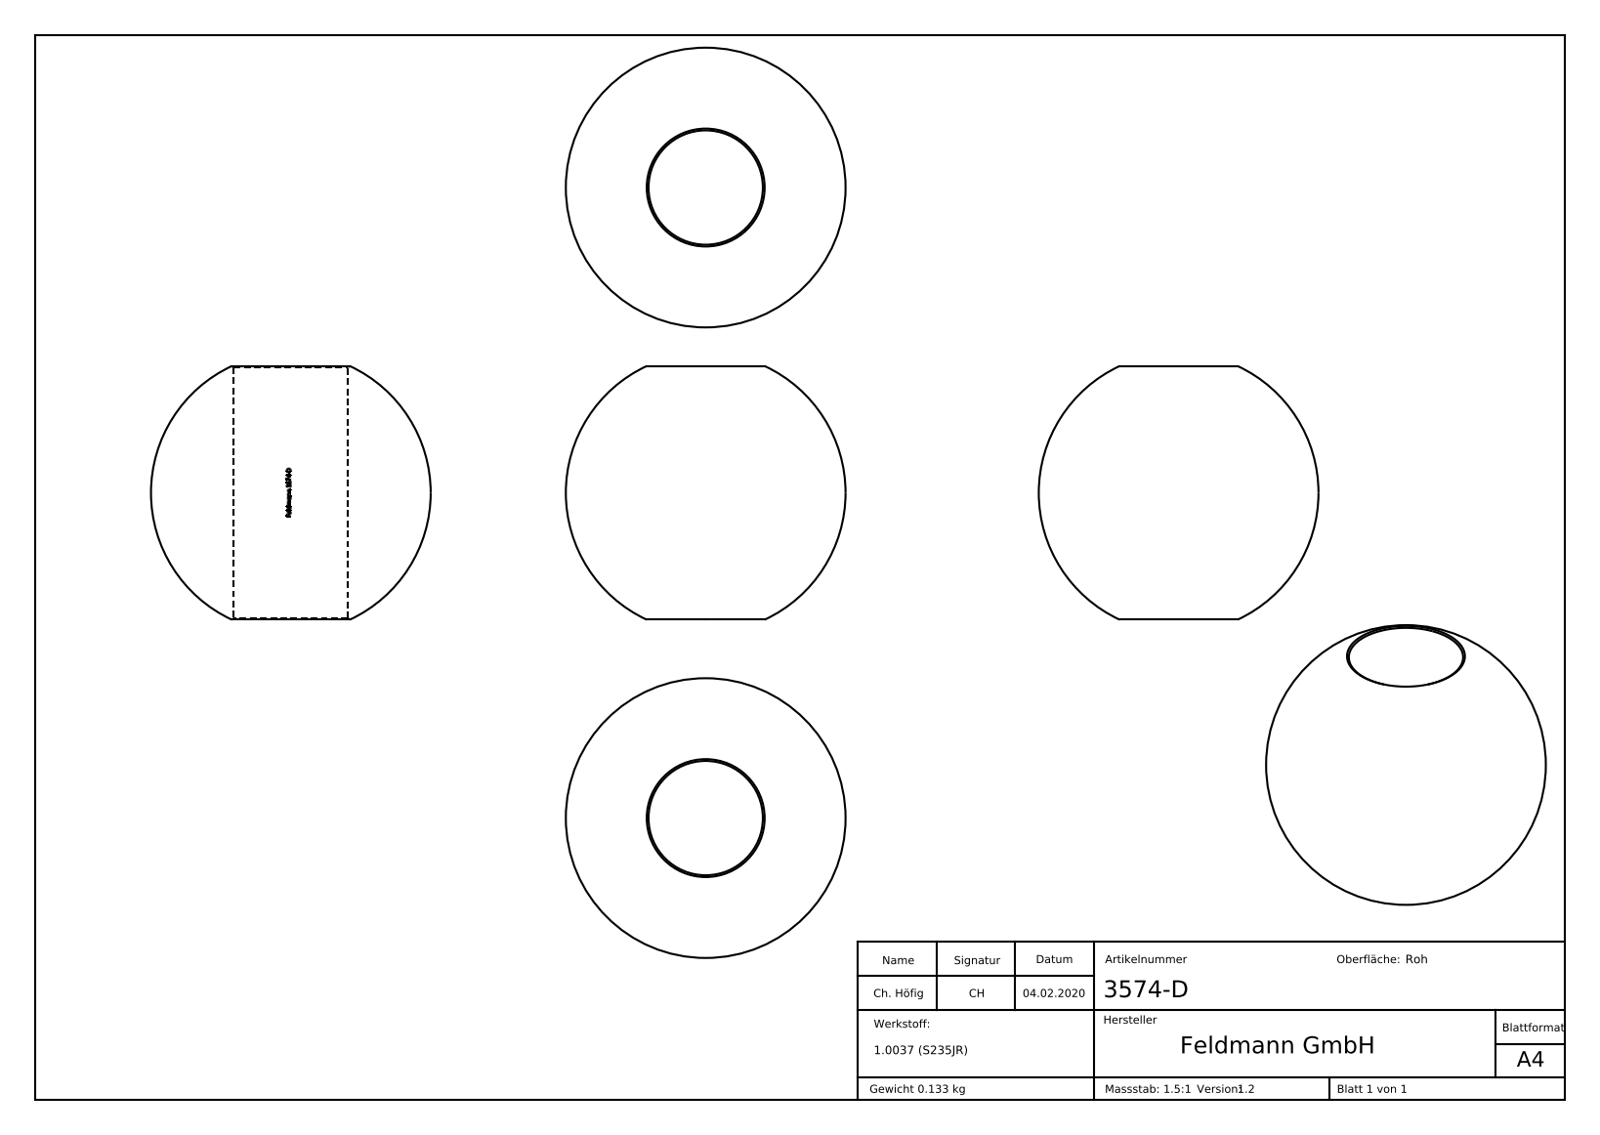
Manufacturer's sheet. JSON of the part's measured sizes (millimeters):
{"part_name": "3574-D", "step_written_by": "SolidWorks 2015 (CONFIG_CONTROL_DESIGN)", "units": "millimeters", "bodies": {"solids": 1, "faces": 192, "planar": 92, "cylindrical": 20, "other": 80}, "overall_size": [35, 35, 31.74], "volume_mm3": 17067, "surface_area_mm2": 4930, "round_holes": [[14.3, 1]], "partial_cylinders_radius": [[7.25, 1]], "face_to_face_distances": [1.19, 2.54, 0.53, 0.35, 0.66, 3.1, 0.5, 0.8, 2.65, 0.45]}
